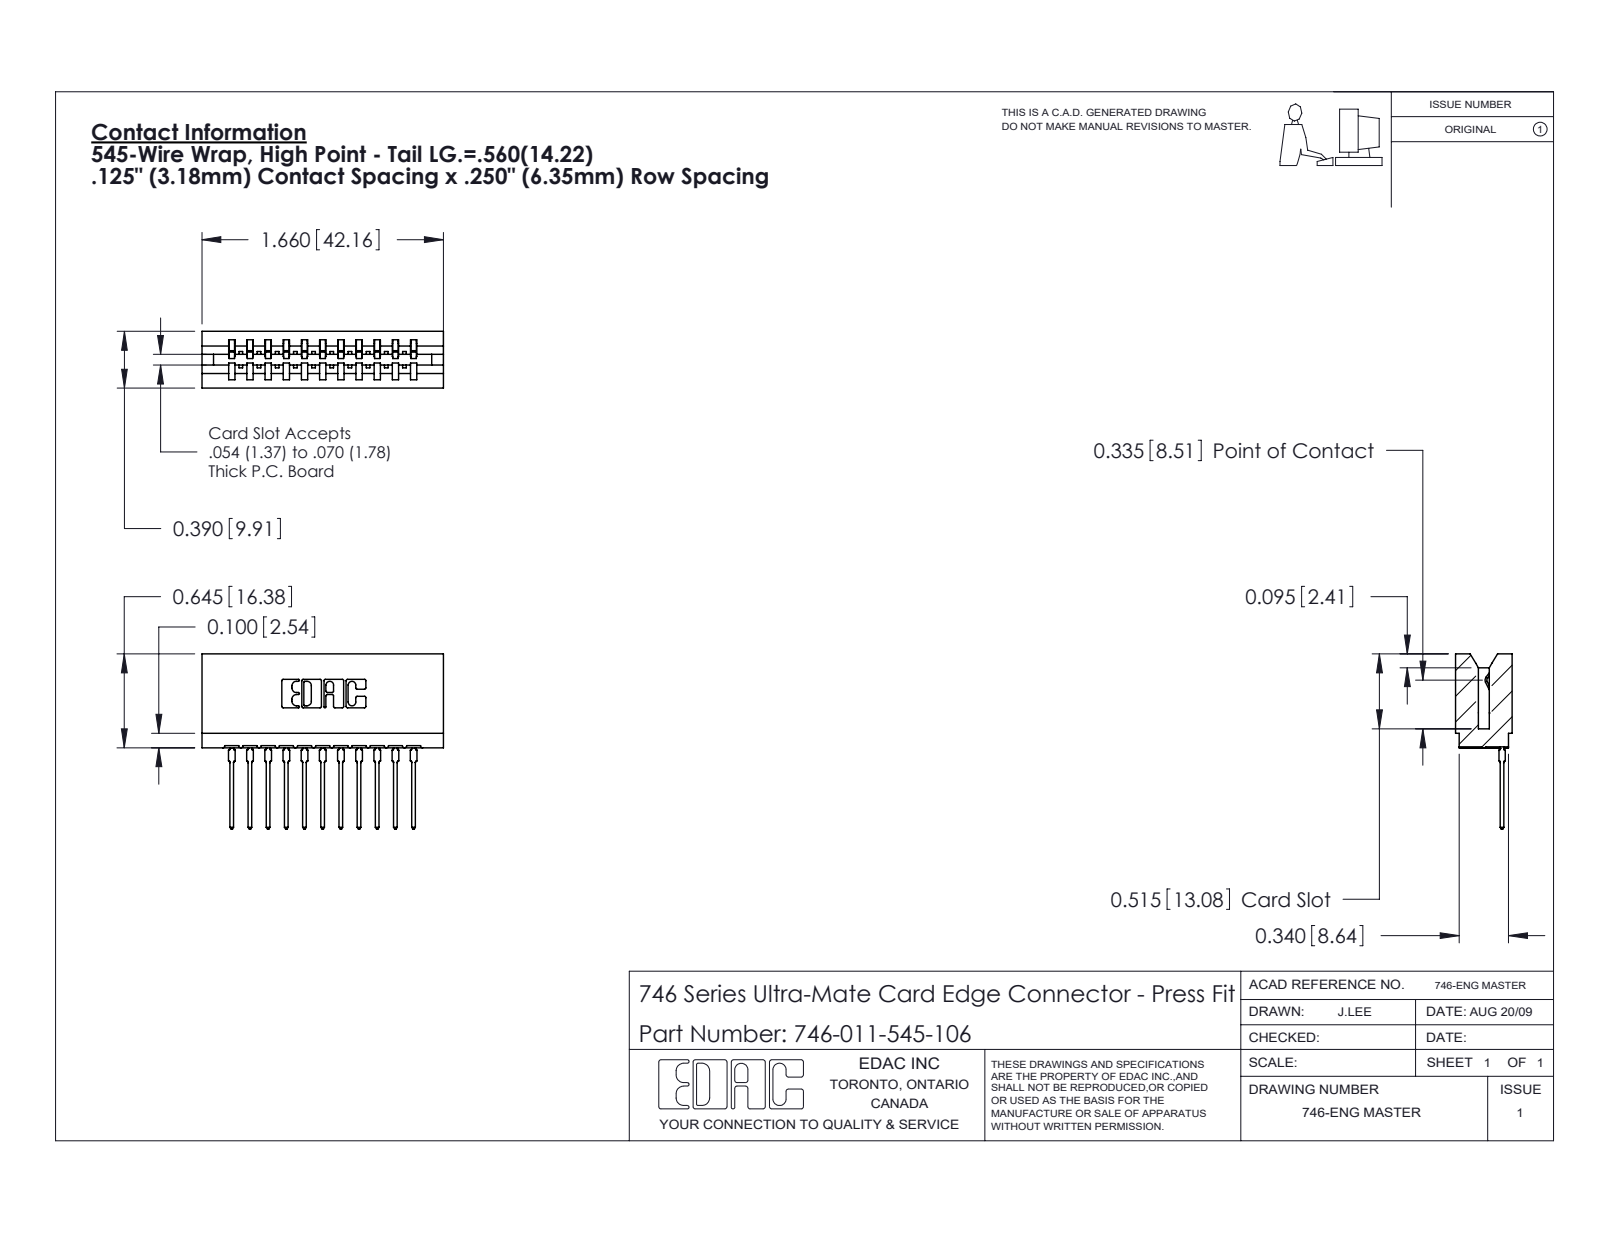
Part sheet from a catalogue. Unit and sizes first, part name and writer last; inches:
Units: inches
Overall size (bounding box): 1.66 × 1.204 × 0.39
Partial cylindrical surfaces — rounded edges, fillets, slot ends (radius × count): R0.01 ×22, R0.021 ×22, R0.015 ×12, R0.007 ×6, R0.031 ×6, R0.005 ×4, R0.011 ×4, R0.026 ×3
Main face-to-face distances: 0.25, 0.333, 0.5, 0.057, 0.125, 0.125, 0.39, 0.042, 0.208, 0.458
Volume: 0.282 in³ · Surface area: 10.08 in²
Bodies: 12 solids, 1286 faces (749 planar, 251 cylindrical, 286 other)
Part name (STEP PRODUCT): 746-292-001_545; 746-011-545-106; 746 Part_.515 Slot Depth - 06
STEP written by: SolidWorks 2020 (CONFIG_CONTROL_DESIGN)
